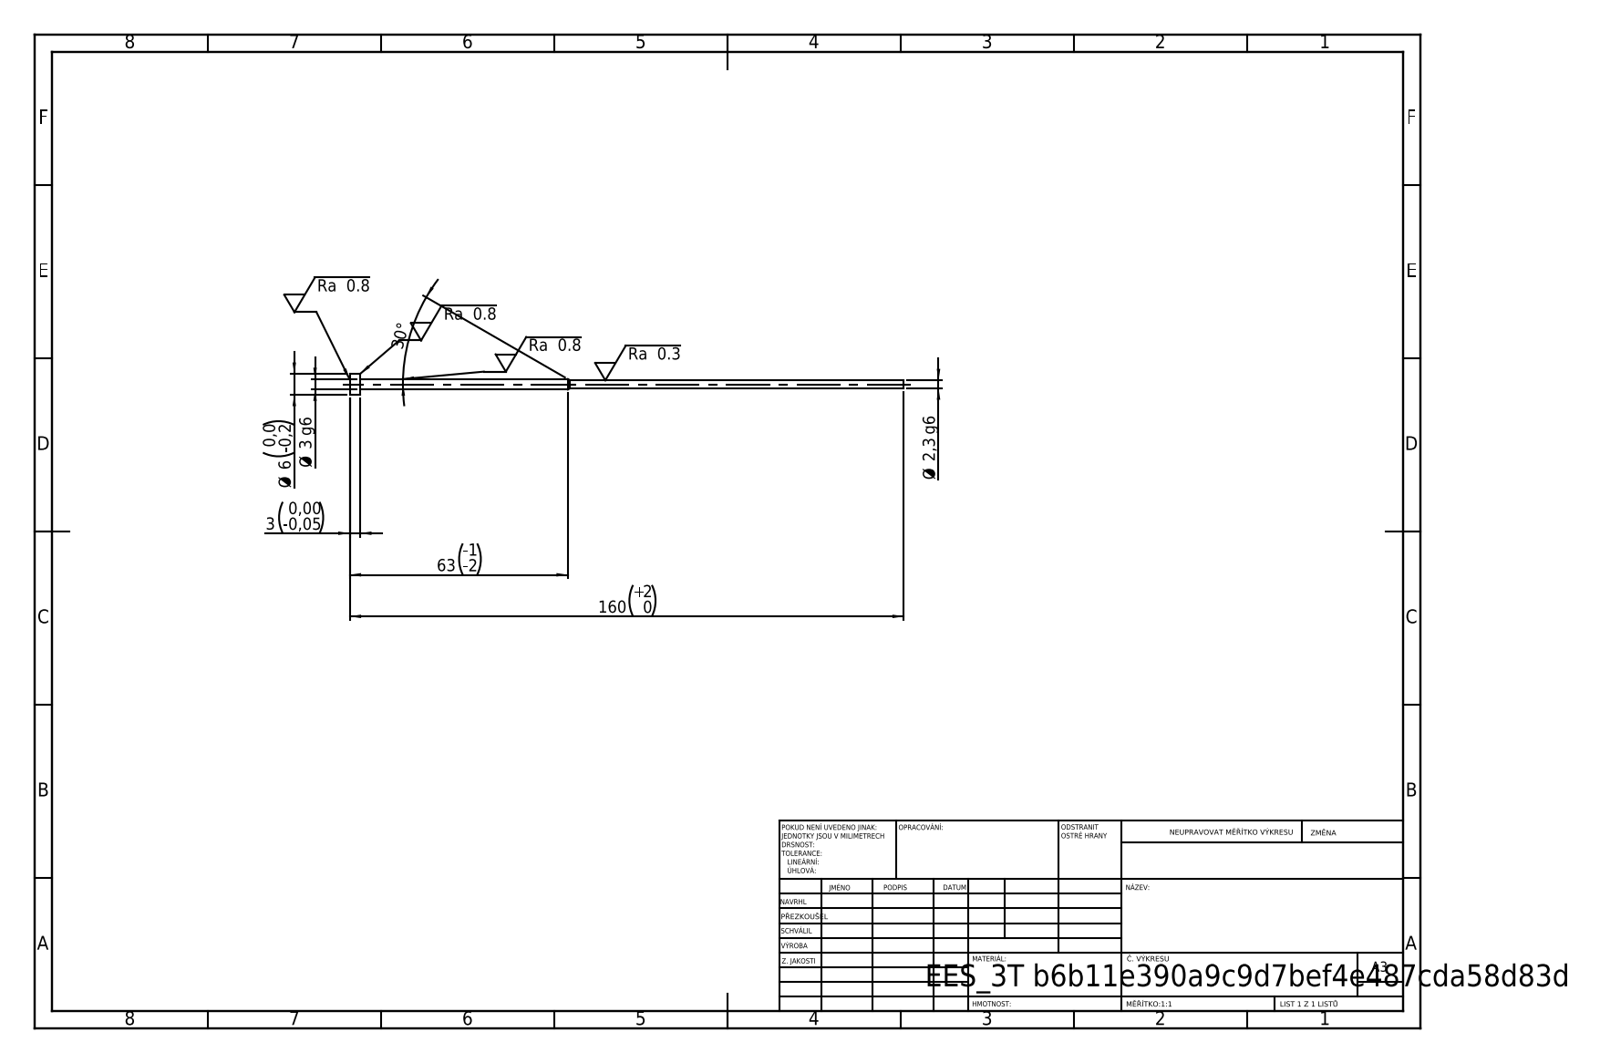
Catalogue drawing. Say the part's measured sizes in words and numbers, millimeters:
Its 3-D file was written by "SolidWorks 2019 (CONFIG_CONTROL_DESIGN)". It is 1 solid with 11 faces: 3 planar, 6 cylindrical and 2 other. Overall it measures 160 by 6 by 6 millimeters. Its volume is 913 cubic millimeters and its surface area 1 378 square millimeters. Round bosses or shafts: 1 of diameter 6, 1 of diameter 3, 1 of diameter 2.3. The main face-to-face distances are 3, 157, 160.
